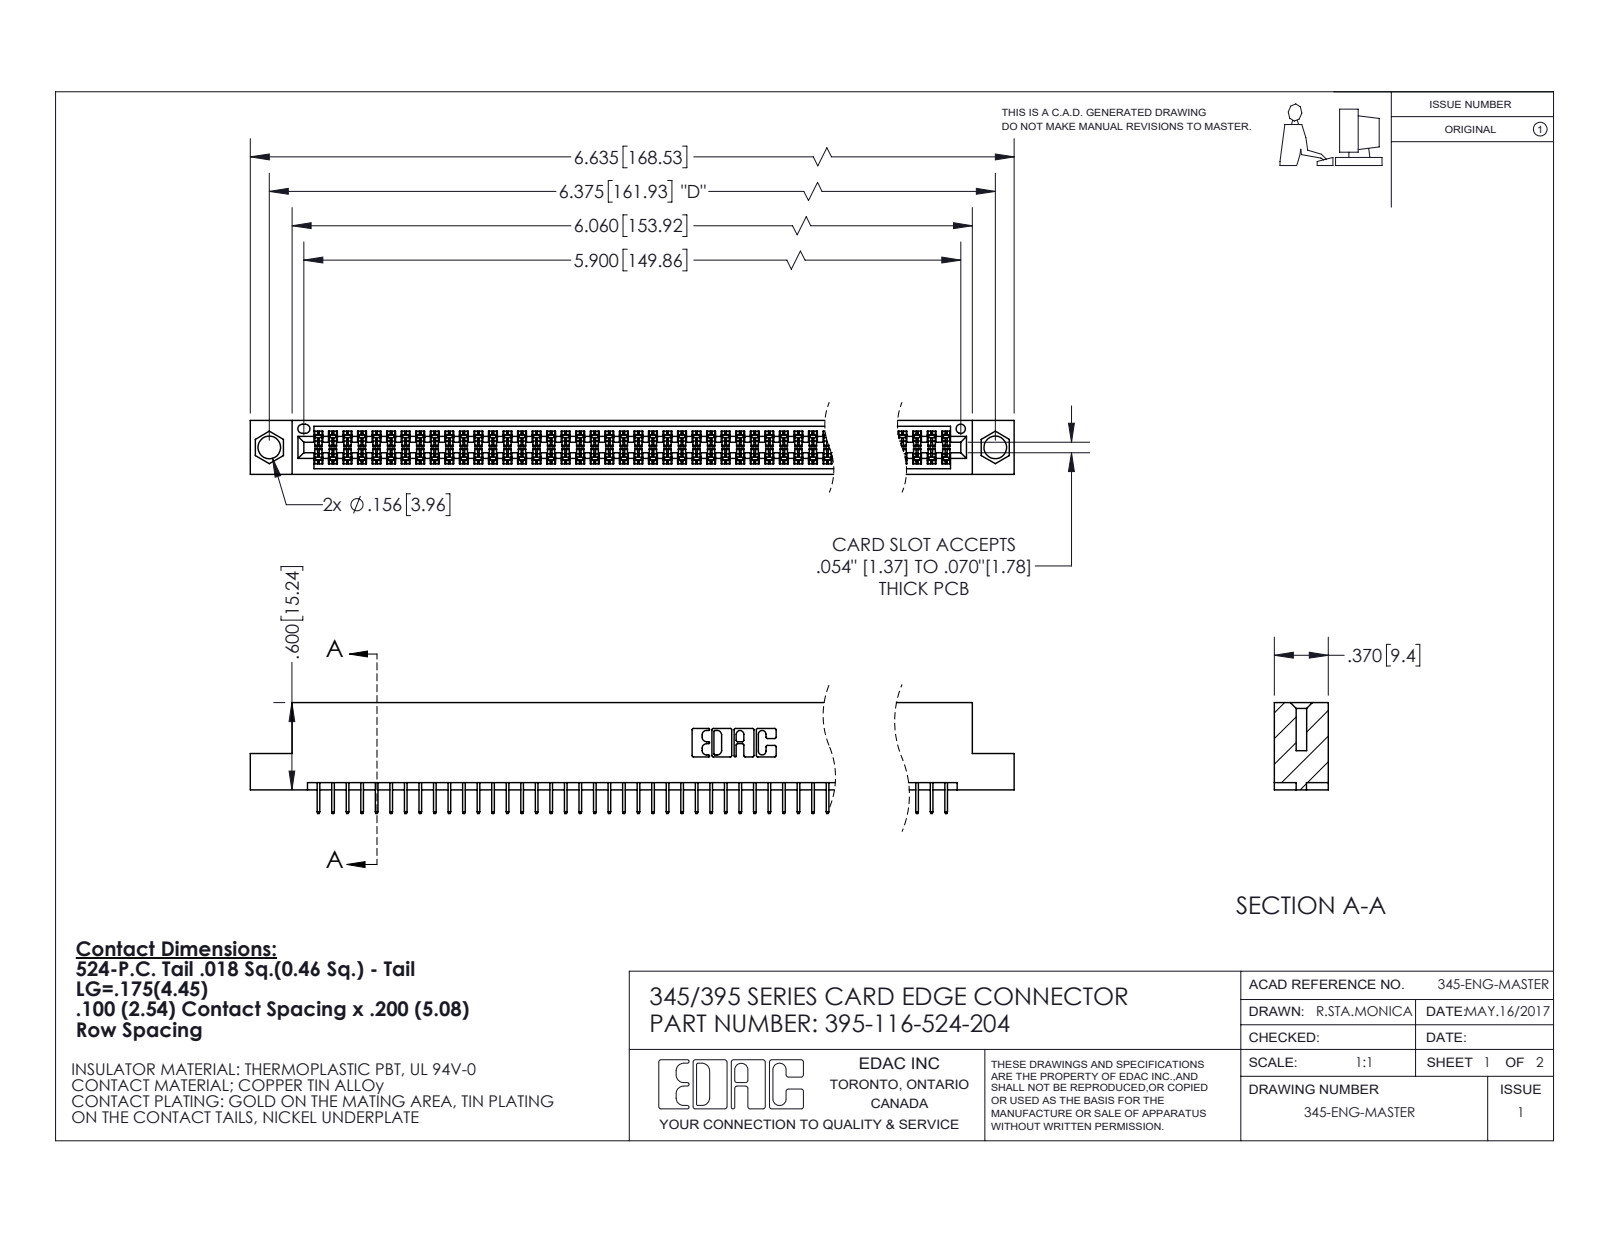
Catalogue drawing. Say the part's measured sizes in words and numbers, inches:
The part is named "395-116-524-204; 345 Part_Flush Mounting Lugs - 0.156 Dia-TI; 345-292-001_345-293-124". Its 3-D file was written by "SolidWorks 2020 (CONFIG_CONTROL_DESIGN)". It is 117 solids with 6404 faces: 4618 planar, 1786 cylindrical and 0 other. Overall it measures 6.635 by 0.762 by 0.37 inches. Its volume is 0.991 cubic inches and its surface area 36.74 square inches. Round holes: 2 of diameter 0.156, 1 of diameter 0.064. Partial cylindrical surfaces (rounded edges, fillets, slot ends): 232 of radius 0.006, 22 of radius 0.01, 6 of radius 0.007, 6 of radius 0.031, 3 of radius 0.026, 2 of radius 0.014, 2 of radius 0.019, 2 of radius 0.022. The main face-to-face distances are 0.072, 0.298, 0.2, 0.37, 0.098, 0.272, 0.025, 0.225, 0.072, 0.175. The hole center spacings are 0.27, 6.139, 6.375.
